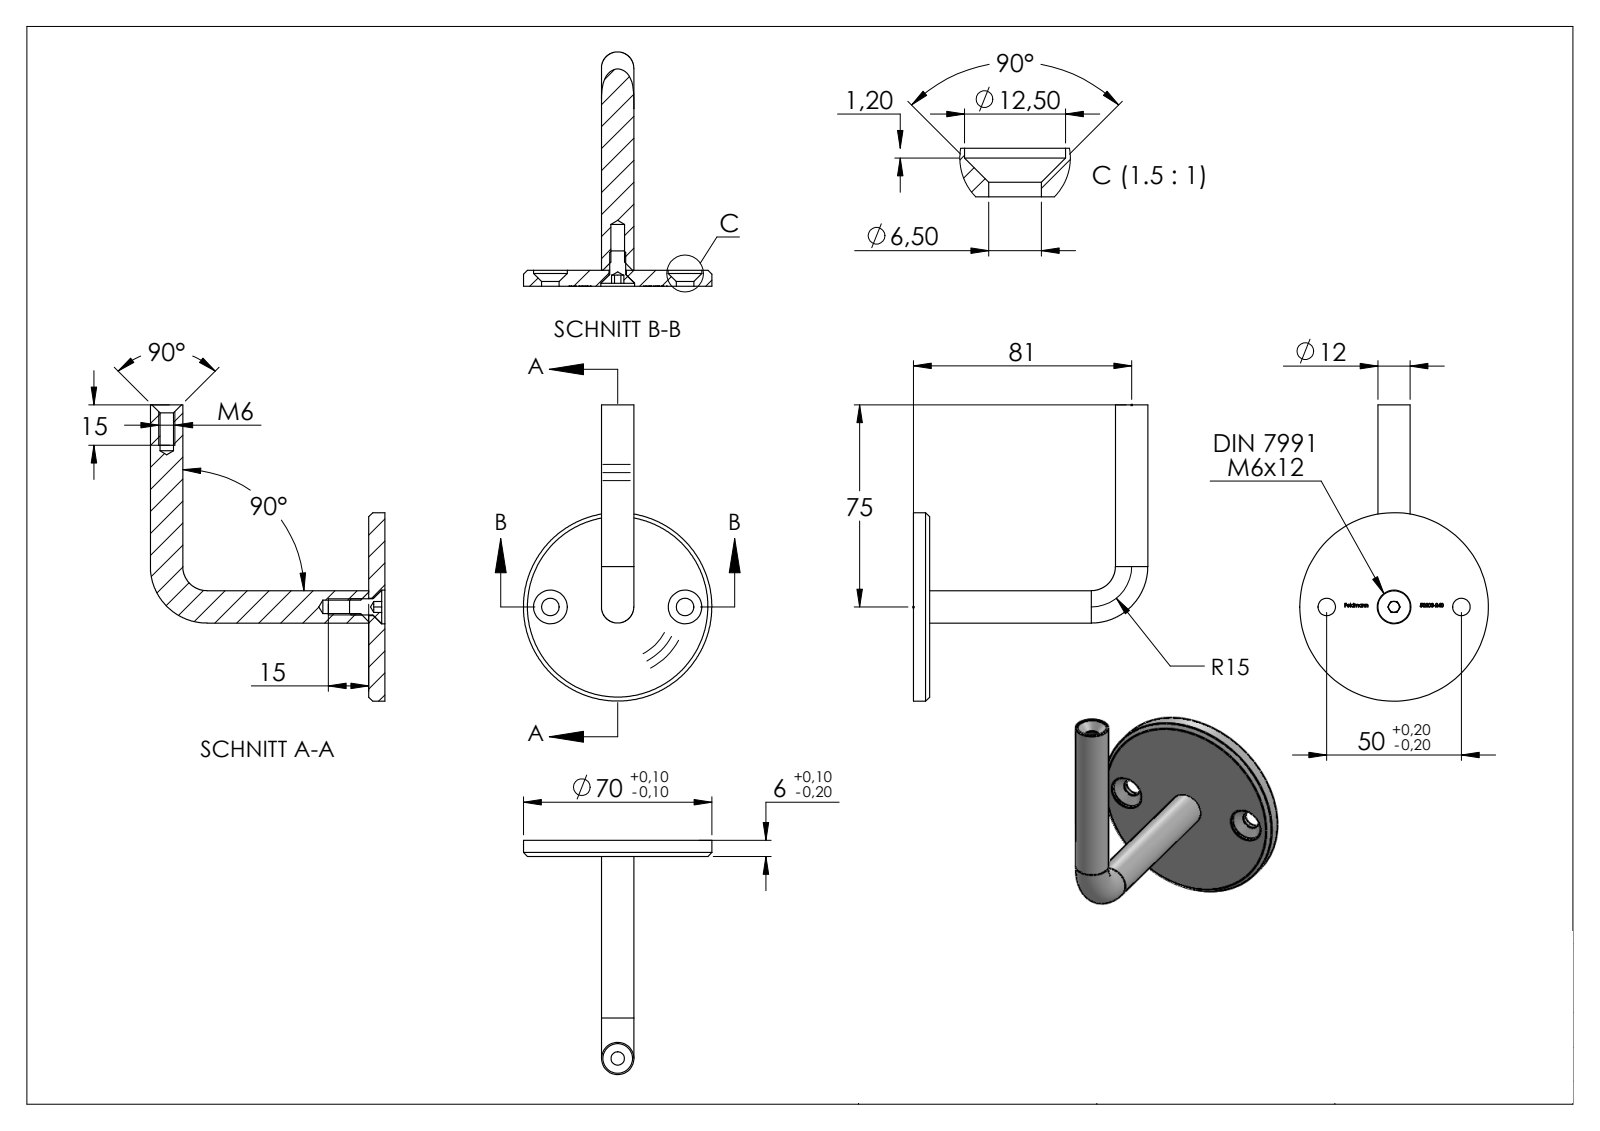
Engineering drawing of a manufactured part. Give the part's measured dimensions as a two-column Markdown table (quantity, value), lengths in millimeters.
| quantity | value |
| --- | --- |
| part name | 50203-240; 50203-240 Teil1_50205-240 Teil1; DIN-7991 M3-M10; 50203-240 Teil2 (+3 more) |
| STEP written by | SolidWorks 2018 (CONFIG_CONTROL_DESIGN) |
| units | millimeters |
| bodies | 3 solids, 293 faces (134 planar, 26 cylindrical, 133 other) |
| overall size | 110 × 87 × 70 |
| volume | 37 345 mm³ |
| surface area | 15 614 mm² |
| round holes (diameter × count) | 6.5 × 3, 12.5 × 3, 5 × 2 |
| round bosses / shafts (diameter × count) | 12 × 2, 70 × 1, 6 × 1 |
| main face-to-face distances | 6, 1.15, 4.85, 4, 13.15, 12, 7.15, 77, 73, 1.05 |
| hole center spacings | 25, 50 |
